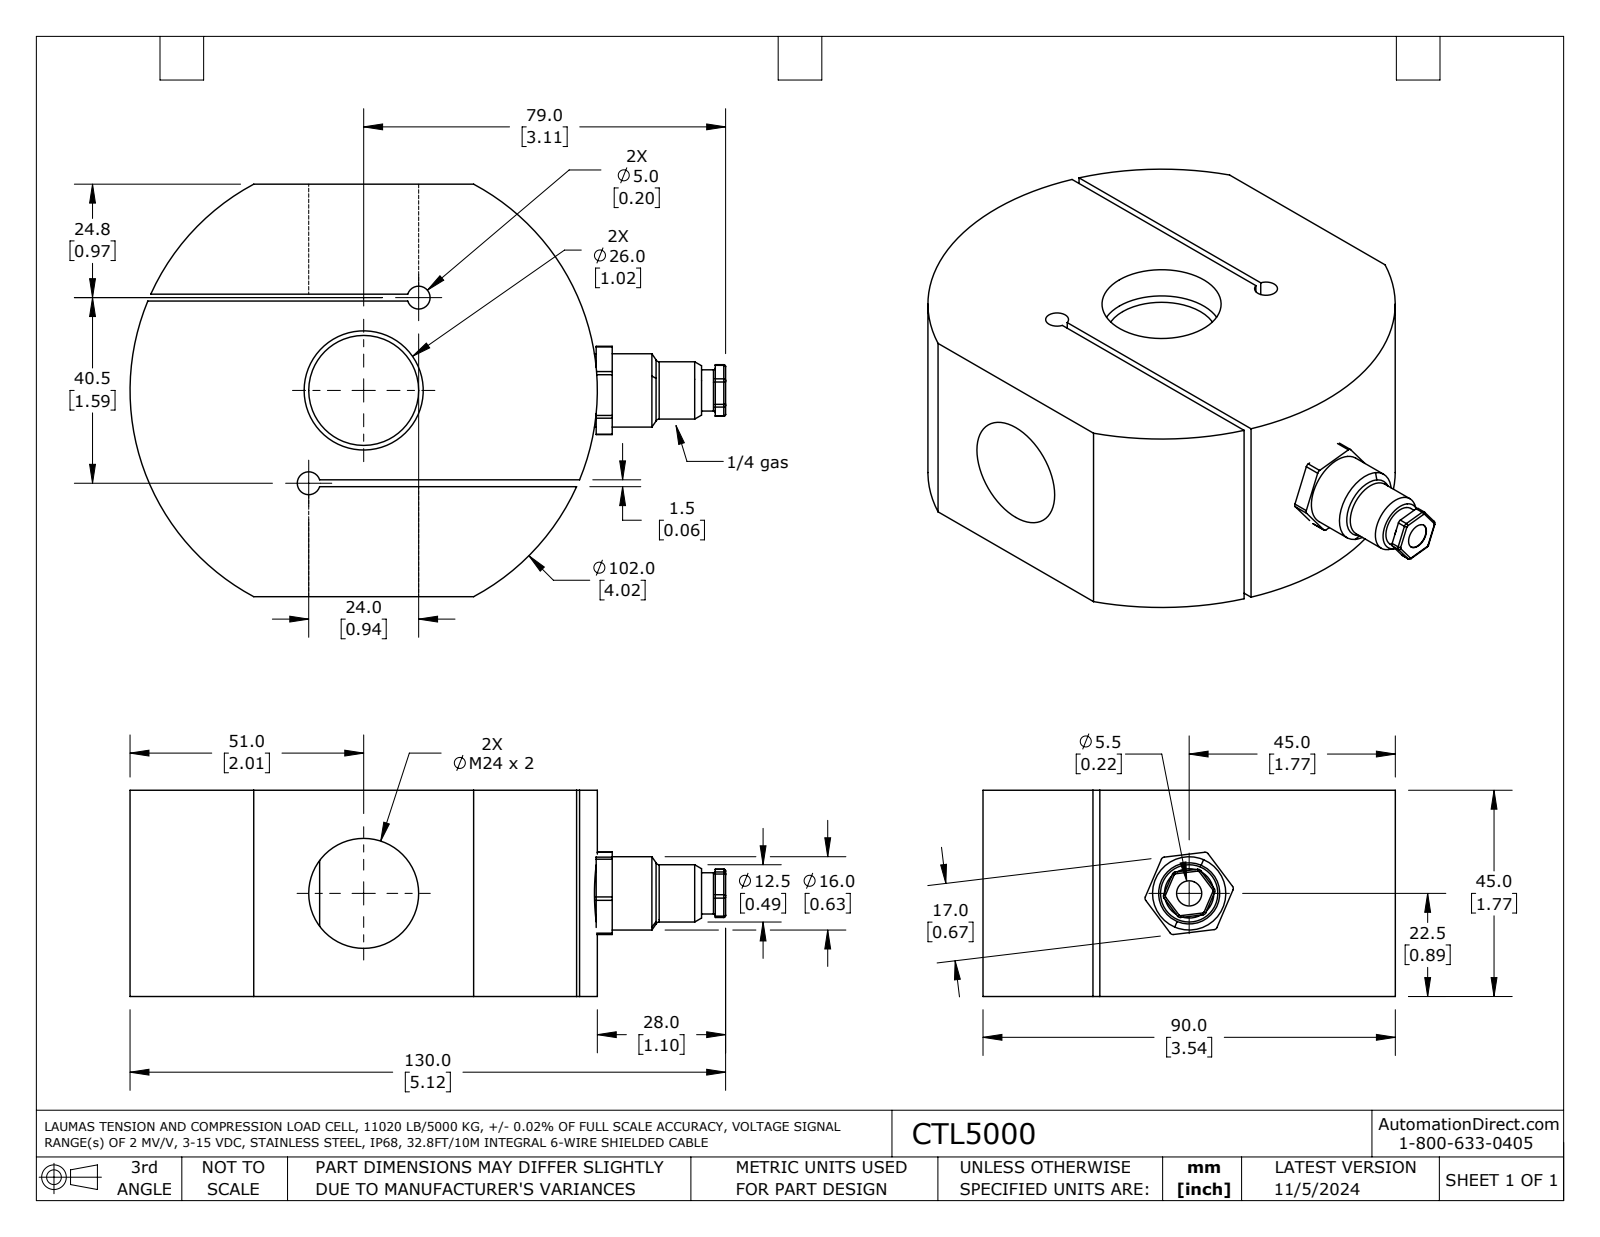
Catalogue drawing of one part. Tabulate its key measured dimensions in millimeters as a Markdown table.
| quantity | value |
| --- | --- |
| part name | CTL5000 |
| STEP written by | SolidWorks 2021 (AUTOMOTIVE_DESIGN) |
| units | millimeters |
| bodies | 2 solids, 100 faces (31 planar, 50 cylindrical, 19 other) |
| overall size | 130 × 90 × 45 |
| volume | 313 200 mm³ |
| surface area | 45 930 mm² |
| round holes (diameter × count) | 5 × 2, 5.5 × 1, 14 × 1, 24 × 1, 26 × 1 |
| round bosses / shafts (diameter × count) | 16 × 1, 12.5 × 1, 9 × 1 |
| partial cylindrical surfaces (radius × count) | 0.8 × 12, 0.4 × 6, 51 × 1 |
| main face-to-face distances | 45, 1.5, 40.5, 24, 25.5, 64.5, 66, 39, 42, 90 |
| hole center spacings | 23.5, 47.1 |
